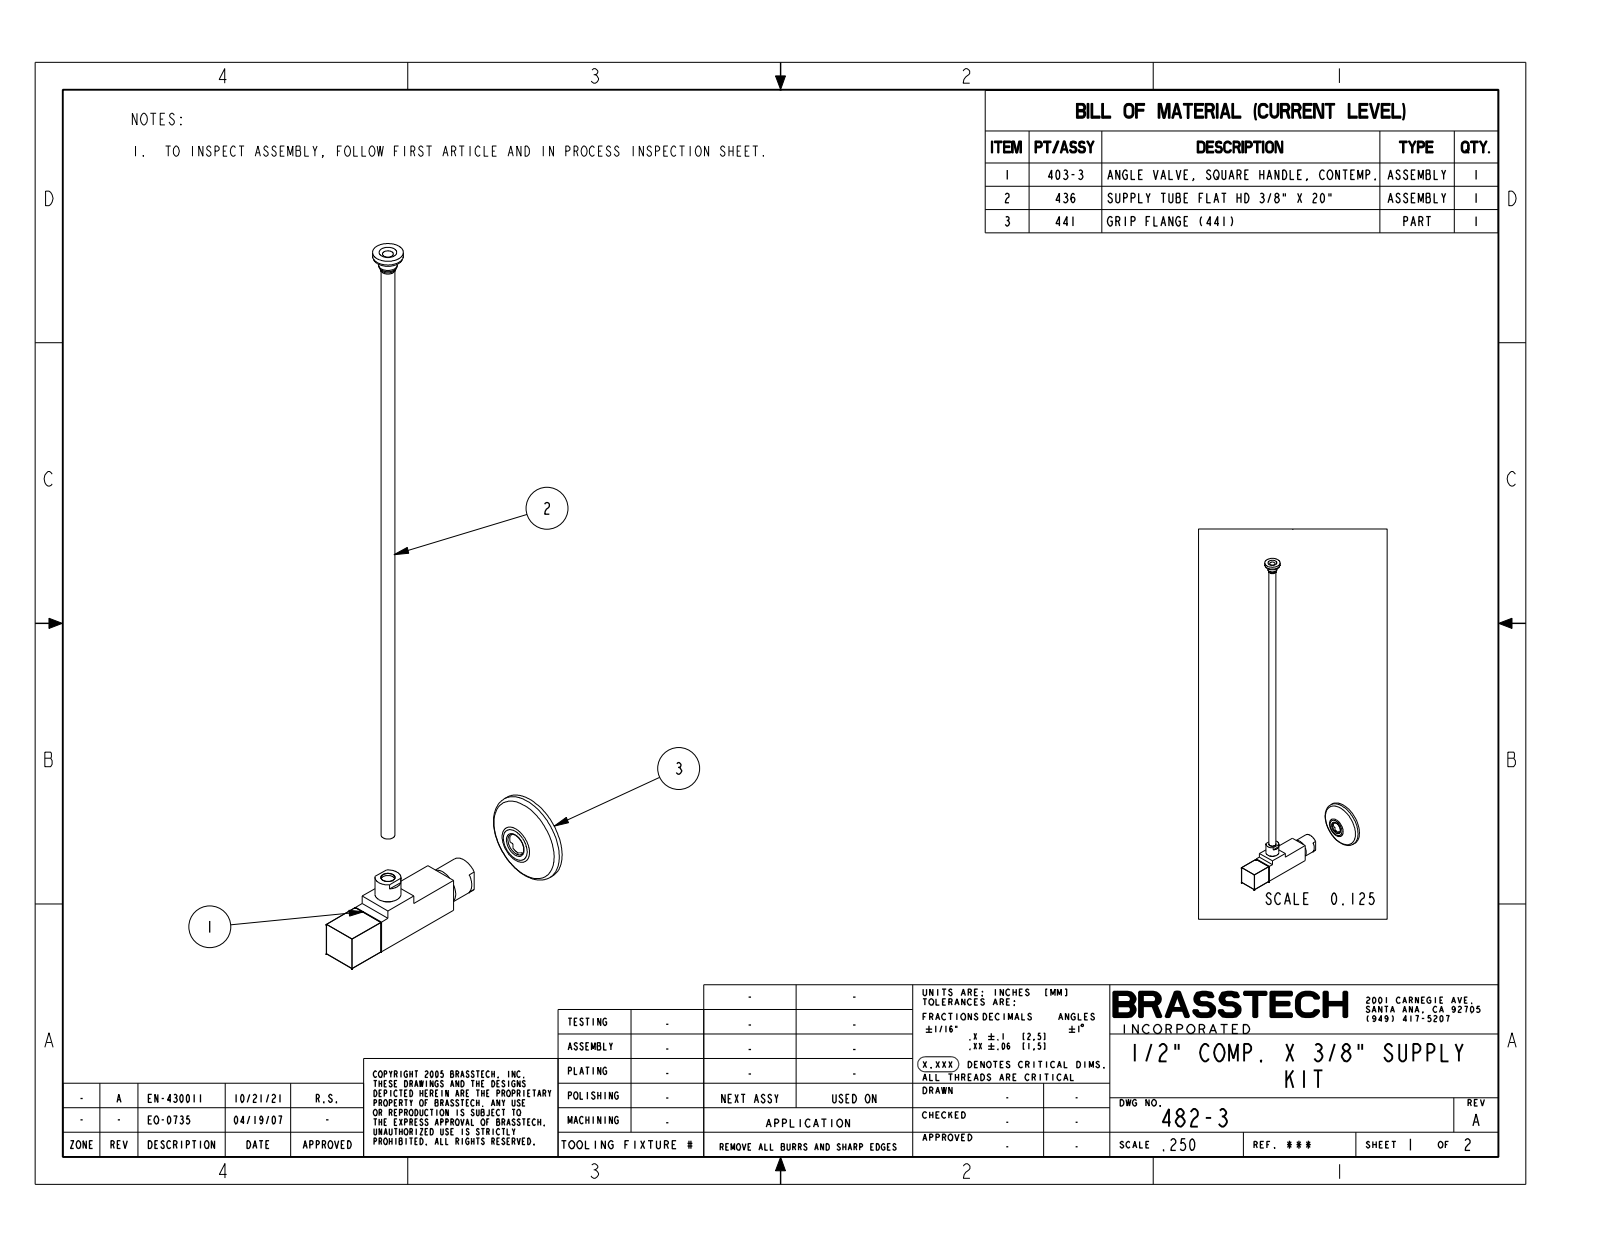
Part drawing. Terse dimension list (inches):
name: 482-3
written by: CREO PARAMETRIC BY PTC INC, 2018500 (CONFIG_CONTROL_DESIGN)
unit: in
bodies: 4 solids, 696 faces (181 planar, 329 cylindrical, 186 other)
size: 21.575 × 7.409 × 2.5
volume: 3.567 in³; area: 164 in²
holes: 2× ⌀0.3, 1× ⌀0.13, 1× ⌀0.272, 1× ⌀0.275, 1× ⌀0.33, 1× ⌀0.335, 1× ⌀0.38, 1× ⌀0.387, 1× ⌀0.39, 1× ⌀0.6, 1× ⌀0.62, 1× ⌀0.625
bosses: 1× ⌀0.906, 1× ⌀0.845, 1× ⌀0.8, 1× ⌀0.717, 1× ⌀0.663, 1× ⌀0.634, 1× ⌀0.63, 1× ⌀0.555
rounds: 14× R0.005, 10× R0.03, 5× R0.058, 1× R0.082, 1× R0.082, 1× R0.199, 1× R0.31
face distances: 1, 1.4, 3.945, 0.894, 4.839, 0.25, 1.25, 3.714, 2.82, 1.125
hole spacings: 0.043, 1.377, 1.42
